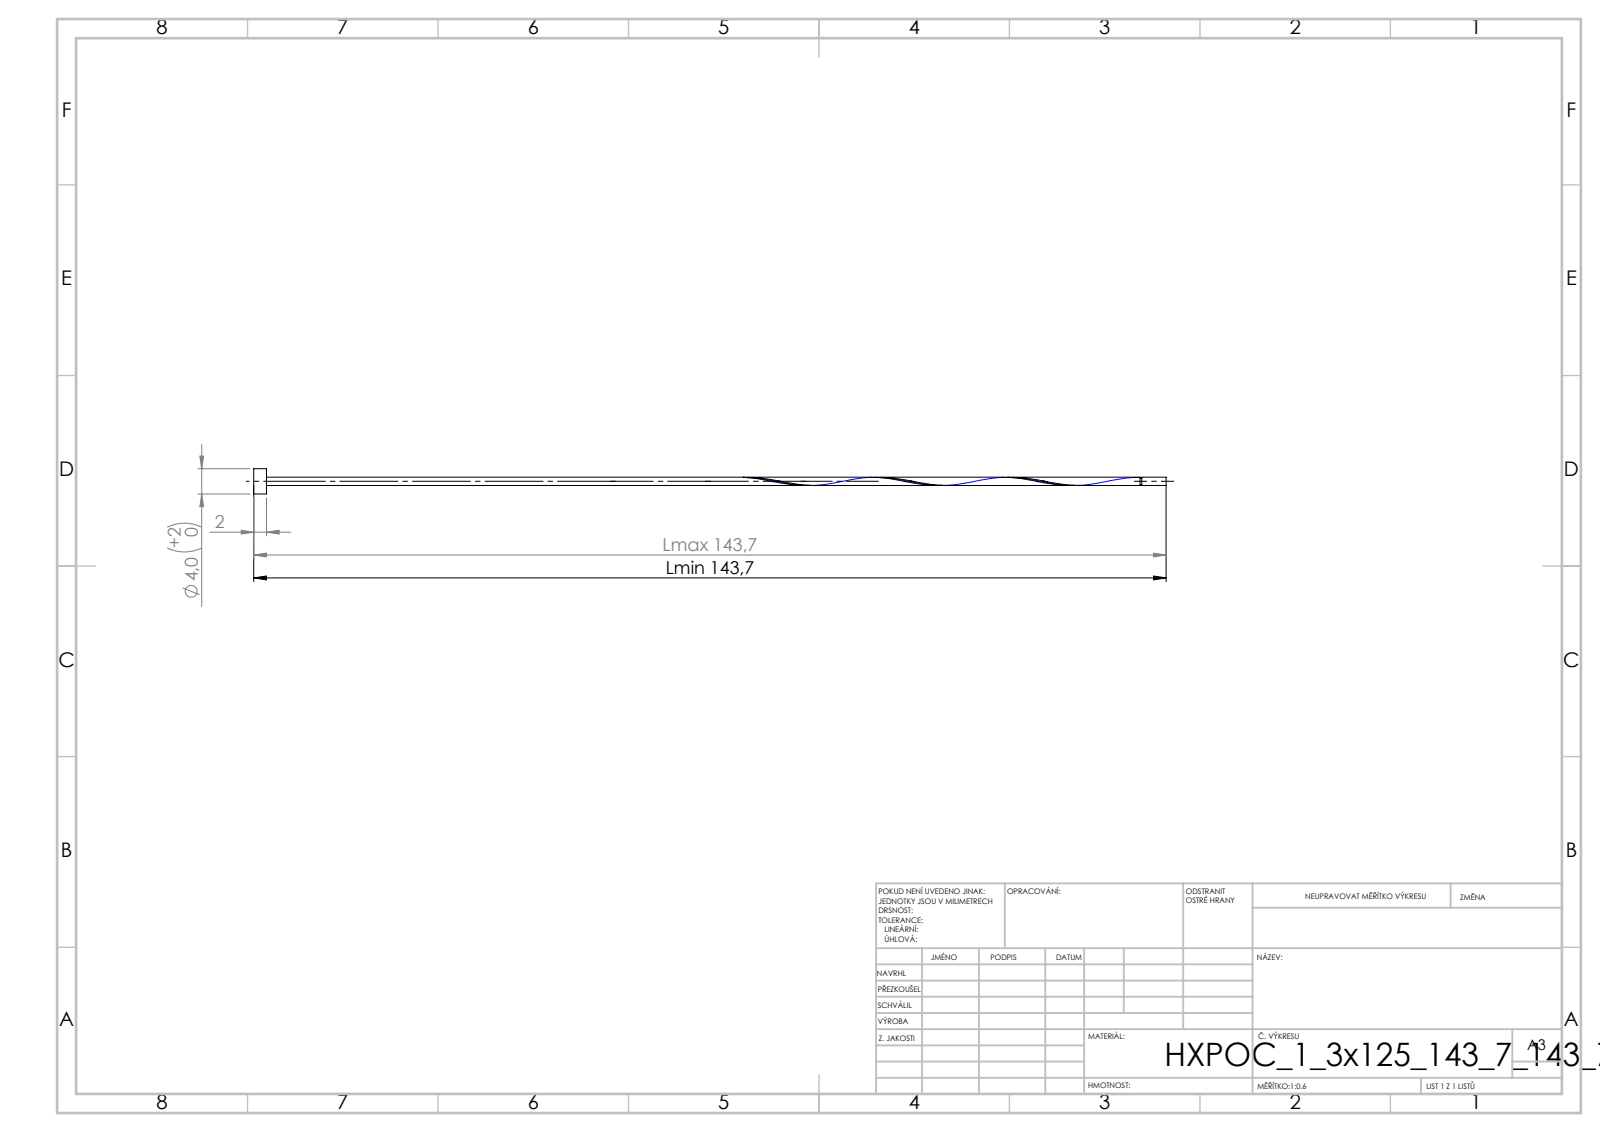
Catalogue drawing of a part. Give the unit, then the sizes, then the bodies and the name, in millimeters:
Units: millimetres
Overall size (bounding box): 143.7 × 4 × 4
Round bosses / shafts (diameter × count): ⌀4 ×1, ⌀1.3 ×1, ⌀1.04 ×1
Main face-to-face distances: 2, 143.7, 141.7, 139.85, 137.85, 3.85, 139.59, 137.59, 4.11, 77.09
Volume: 248 mm³ · Surface area: 808 mm²
Bodies: 1 solid, 16 faces (6 planar, 9 cylindrical, 1 other)
STEP written by: SolidWorks 2019 (CONFIG_CONTROL_DESIGN)
